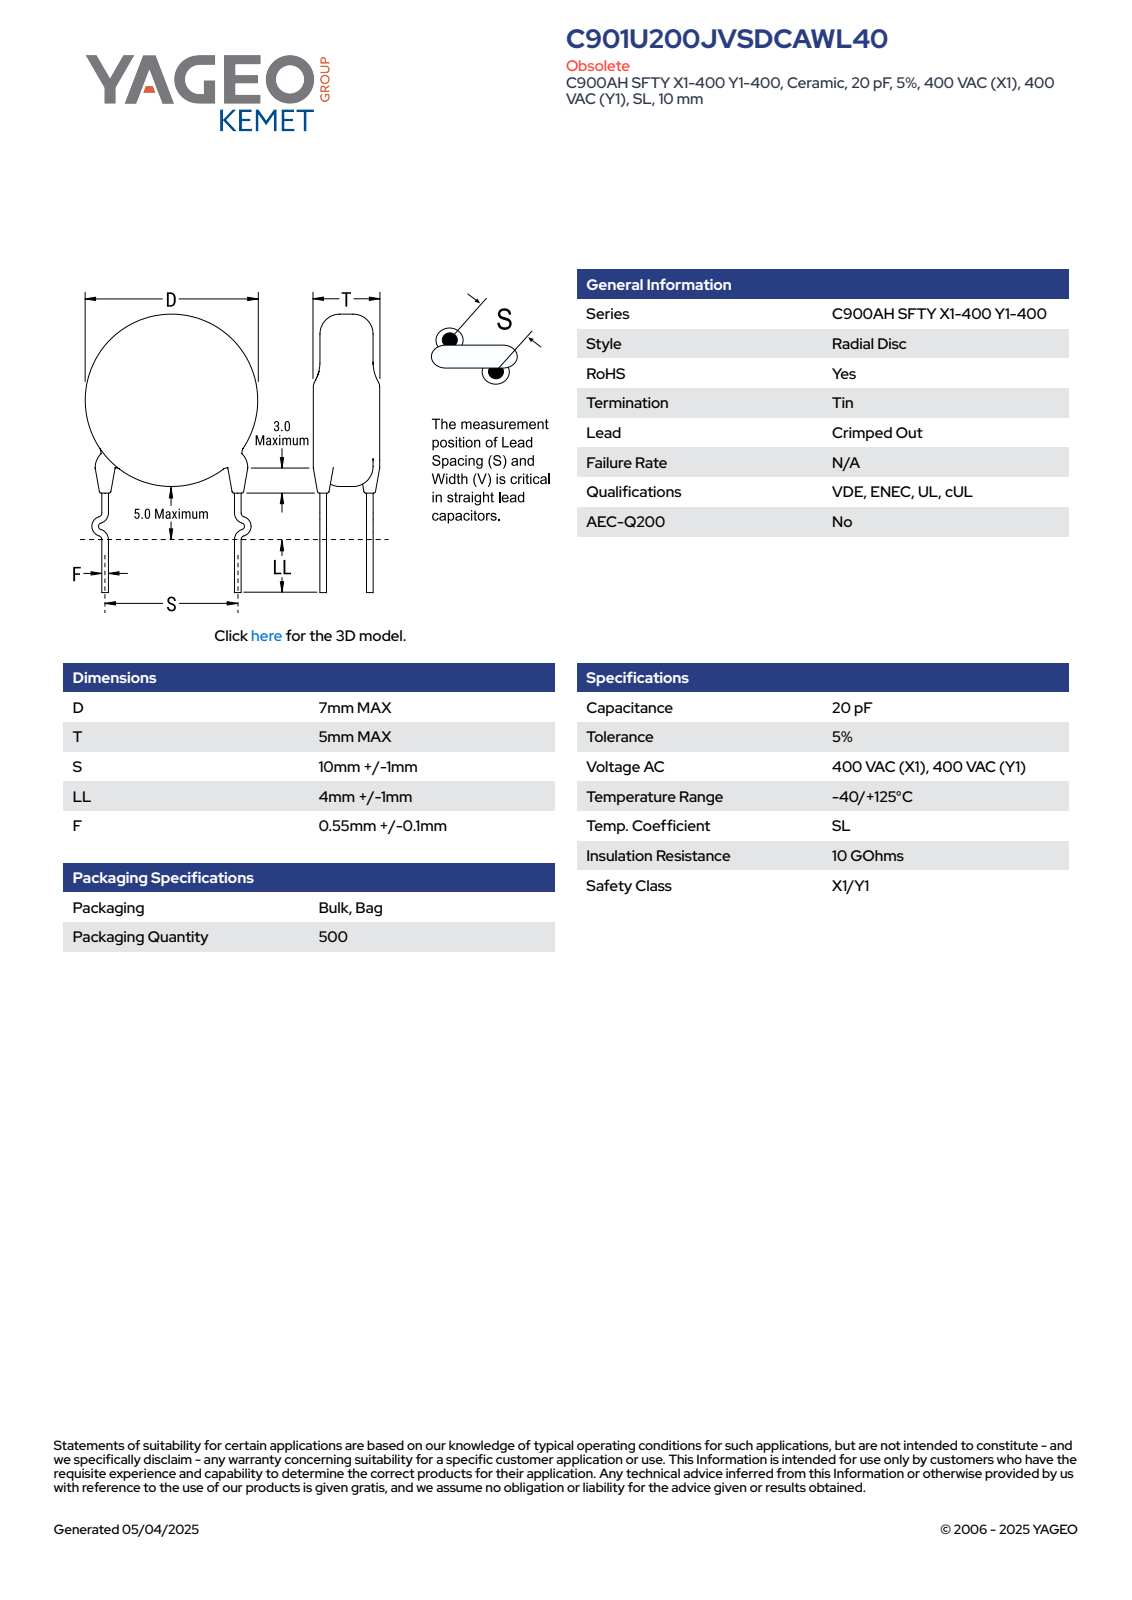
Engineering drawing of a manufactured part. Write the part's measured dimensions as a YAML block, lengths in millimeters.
part_name: "CCD_KCOC900_D7T5S10LL5F0.55"
step_written_by: "SolidWorks 2014 (AUTOMOTIVE_DESIGN)"
units: millimeters
bodies: {solids: 4, faces: 93, planar: 63, cylindrical: 10, other: 20}
overall_size: [17, 13.89, 6.87]
volume: 199
surface_area: 245
round_bosses_or_shafts:
  - {diameter: 1.2, count: 4}
  - {diameter: 7, count: 1}
face_to_face_distances: [5, 0.73, 3.87, 3.14, 0.59, 0.32, 2.97, 1.5, 2.16, 2.24]
